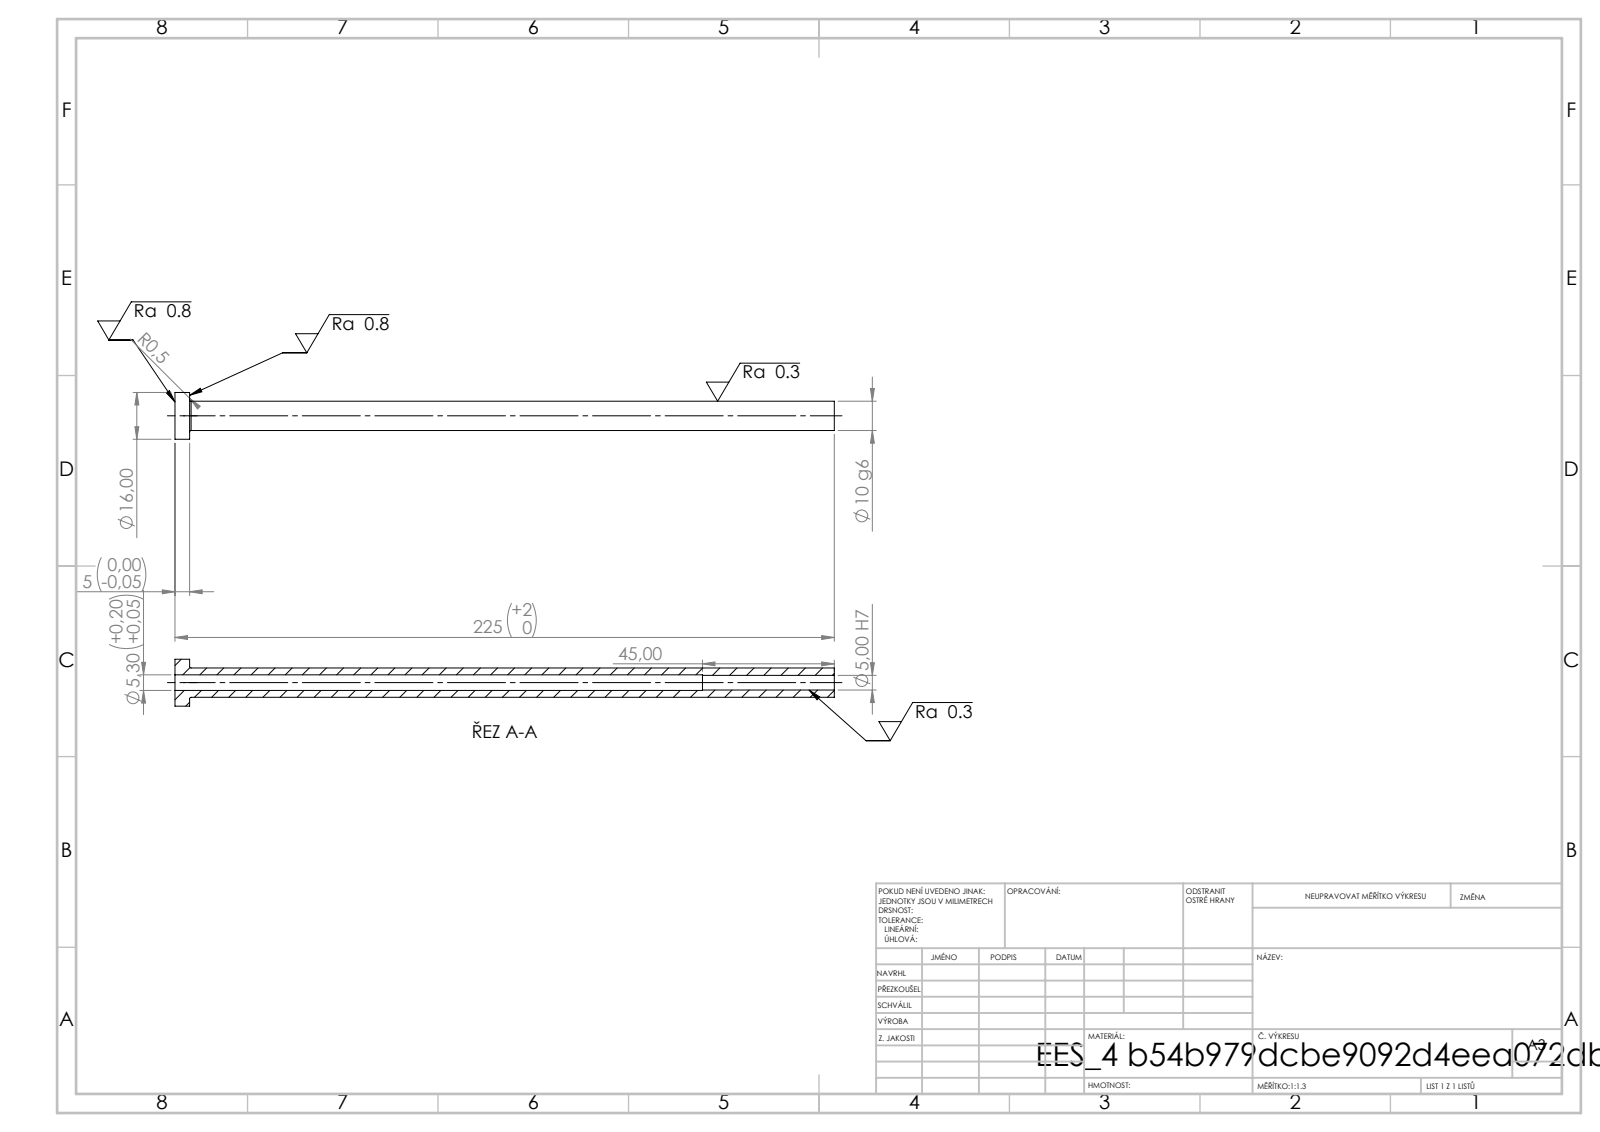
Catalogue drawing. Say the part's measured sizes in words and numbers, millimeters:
Its 3-D file was written by "SolidWorks 2019 (CONFIG_CONTROL_DESIGN)". It is 1 solid with 14 faces: 4 planar, 8 cylindrical and 2 other. Overall it measures 225 by 16 by 16 millimeters. Its volume is 13 431 cubic millimeters and its surface area 11 223 square millimeters. Round holes: 1 of diameter 5, 1 of diameter 5.3. Round bosses or shafts: 1 of diameter 16, 1 of diameter 10. The main face-to-face distances are 5, 225, 220, 180, 175, 45.
